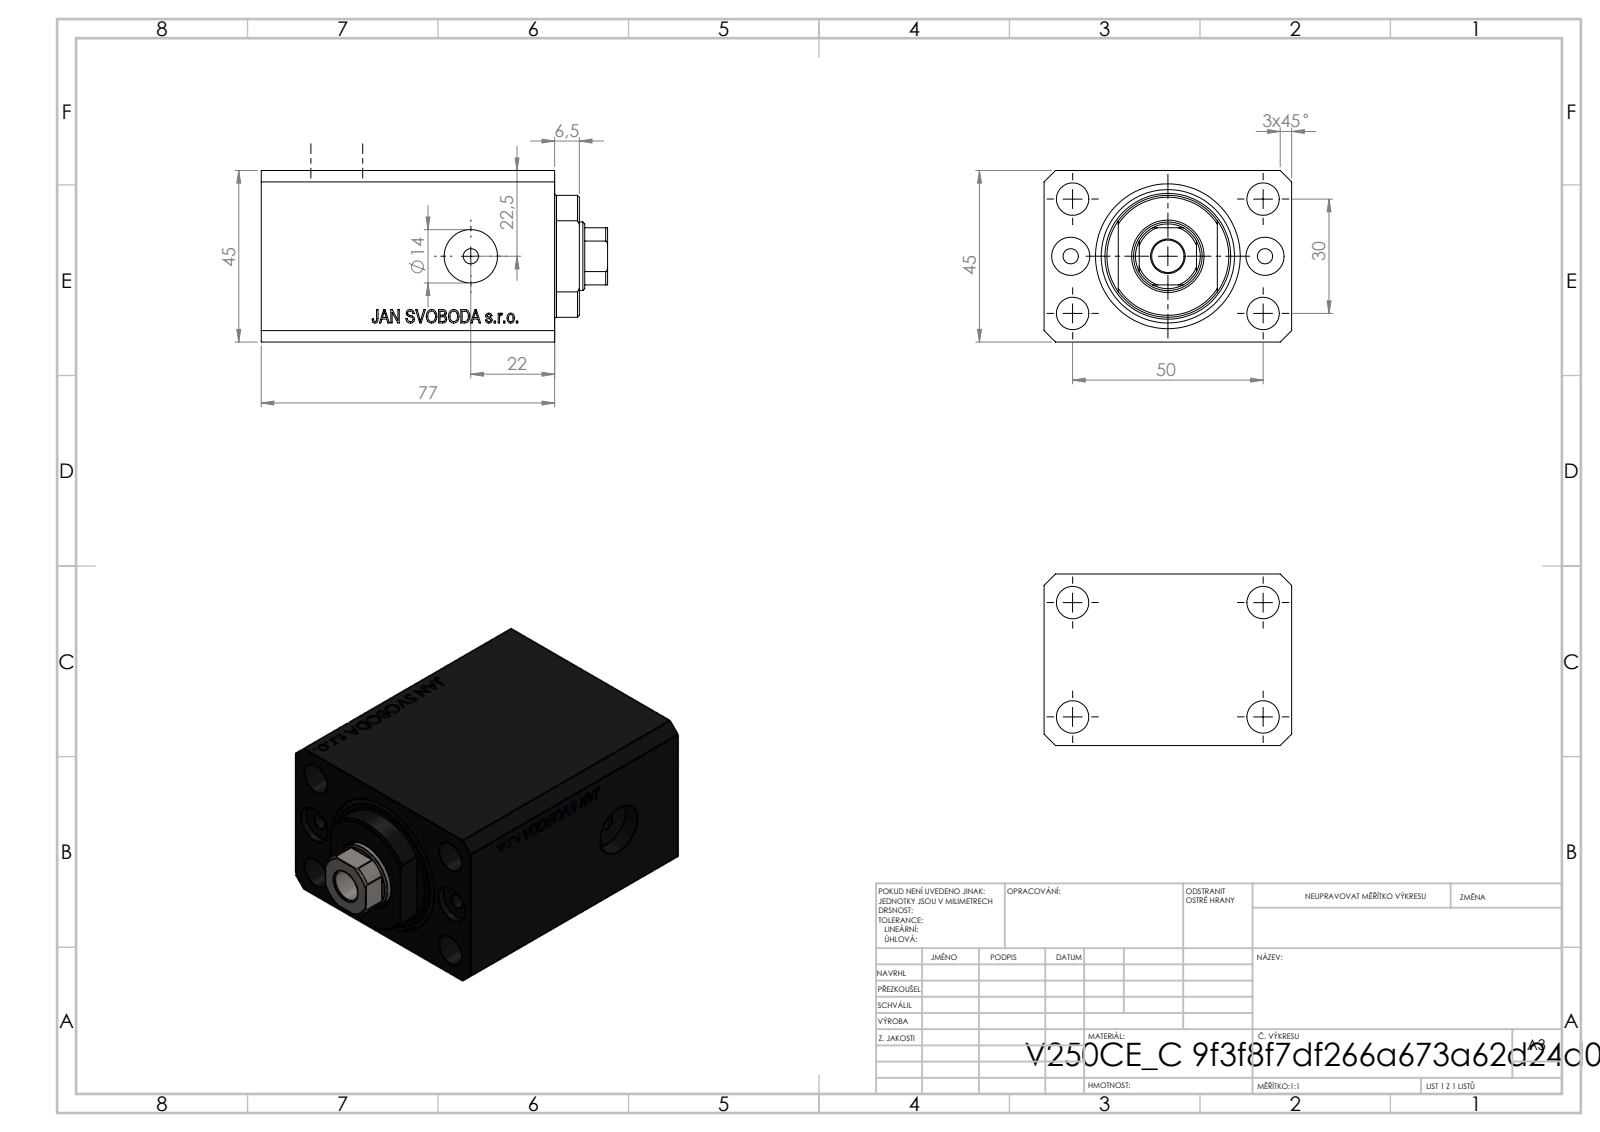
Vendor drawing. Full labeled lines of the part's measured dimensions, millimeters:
Part name (STEP PRODUCT): V250CE_C_Body; V250CE_C_VCP; V250CE_VC_C
STEP written by: SolidWorks 2019 (CONFIG_CONTROL_DESIGN)
Units: millimetres
Bodies: 3 solids, 863 faces (427 planar, 44 cylindrical, 392 other)
Overall size (bounding box): 90.9 × 65 × 45
Volume: 203 828 mm³ · Surface area: 52 497 mm²
Round holes (diameter × count): ⌀8.5 ×5, ⌀4 ×4, ⌀10 ×2, ⌀14 ×2, ⌀18 ×1, ⌀25 ×1, ⌀38 ×1
Partial cylindrical surfaces — rounded edges, fillets, slot ends (radius × count): R8.5 ×1, R16 ×1
Main face-to-face distances: 45, 65, 51.9, 77, 25.1, 6.9, 70.1, 73.52, 6.5, 83.5
Hole centre spacings: 15.01, 29.15, 52.68, 25.5, 30, 50, 58.31, 33
